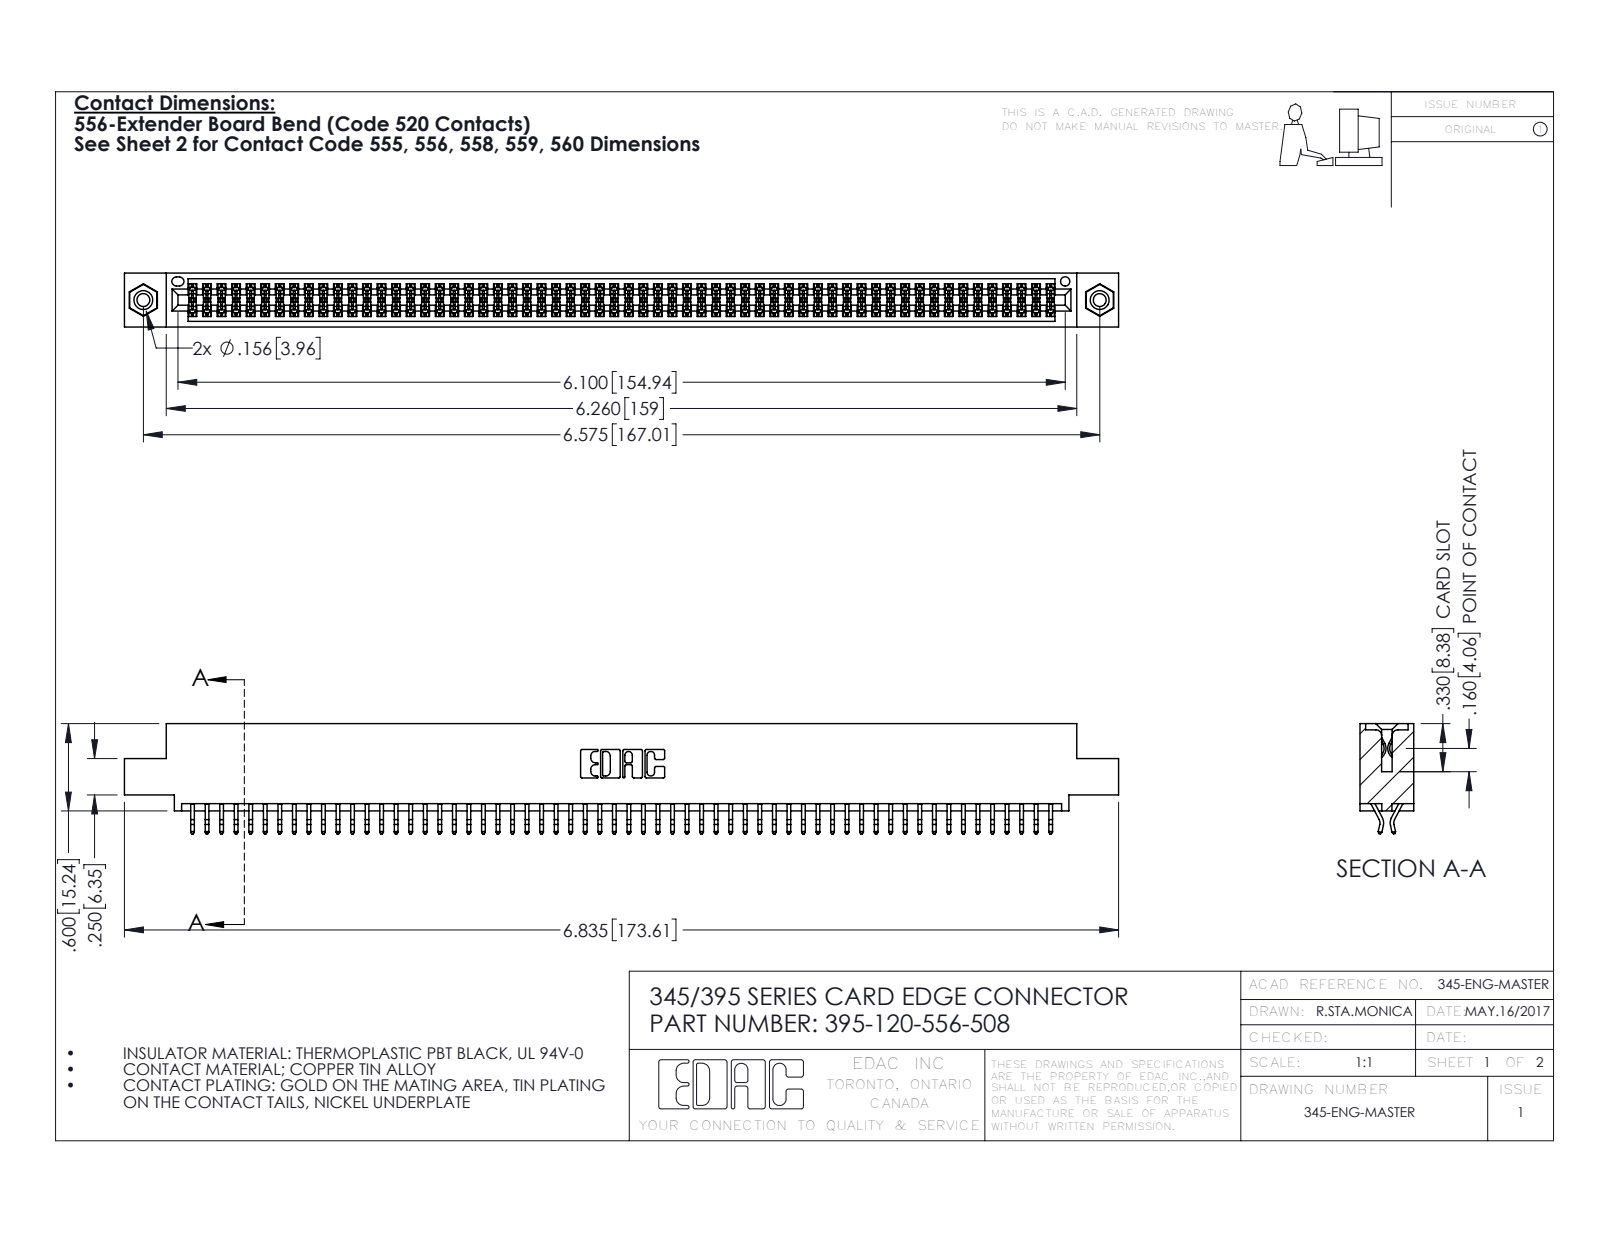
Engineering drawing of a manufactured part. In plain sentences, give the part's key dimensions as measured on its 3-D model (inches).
The part is named "345-292-001_556 Tail; 345-250-001_345-250-003-102; 395-120-556-508; 345 Part_0.110 Offset - 0.156 Dia-TI". Its 3-D file was written by "SolidWorks 2016 (CONFIG_CONTROL_DESIGN)". It is 123 solids with 6910 faces: 4556 planar, 2338 cylindrical and 16 other. Overall it measures 6.835 by 0.757 by 0.37 inches. Its volume is 1.034 cubic inches and its surface area 39.37 square inches. Round holes: 2 of diameter 0.089, 2 of diameter 0.125, 2 of diameter 0.156, 1 of diameter 0.064. Round bosses or shafts: 2 of diameter 0.155. Partial cylindrical surfaces (rounded edges, fillets, slot ends): 180 of radius 0.006, 22 of radius 0.01, 6 of radius 0.007, 6 of radius 0.031, 3 of radius 0.026, 2 of radius 0.01, 2 of radius 0.014, 2 of radius 0.019. The main face-to-face distances are 0.072, 0.298, 0.37, 0.2, 0.025, 0.098, 0.272, 0.225, 0.175, 0.149. The hole center spacings are 0.27, 6.339, 6.575.
